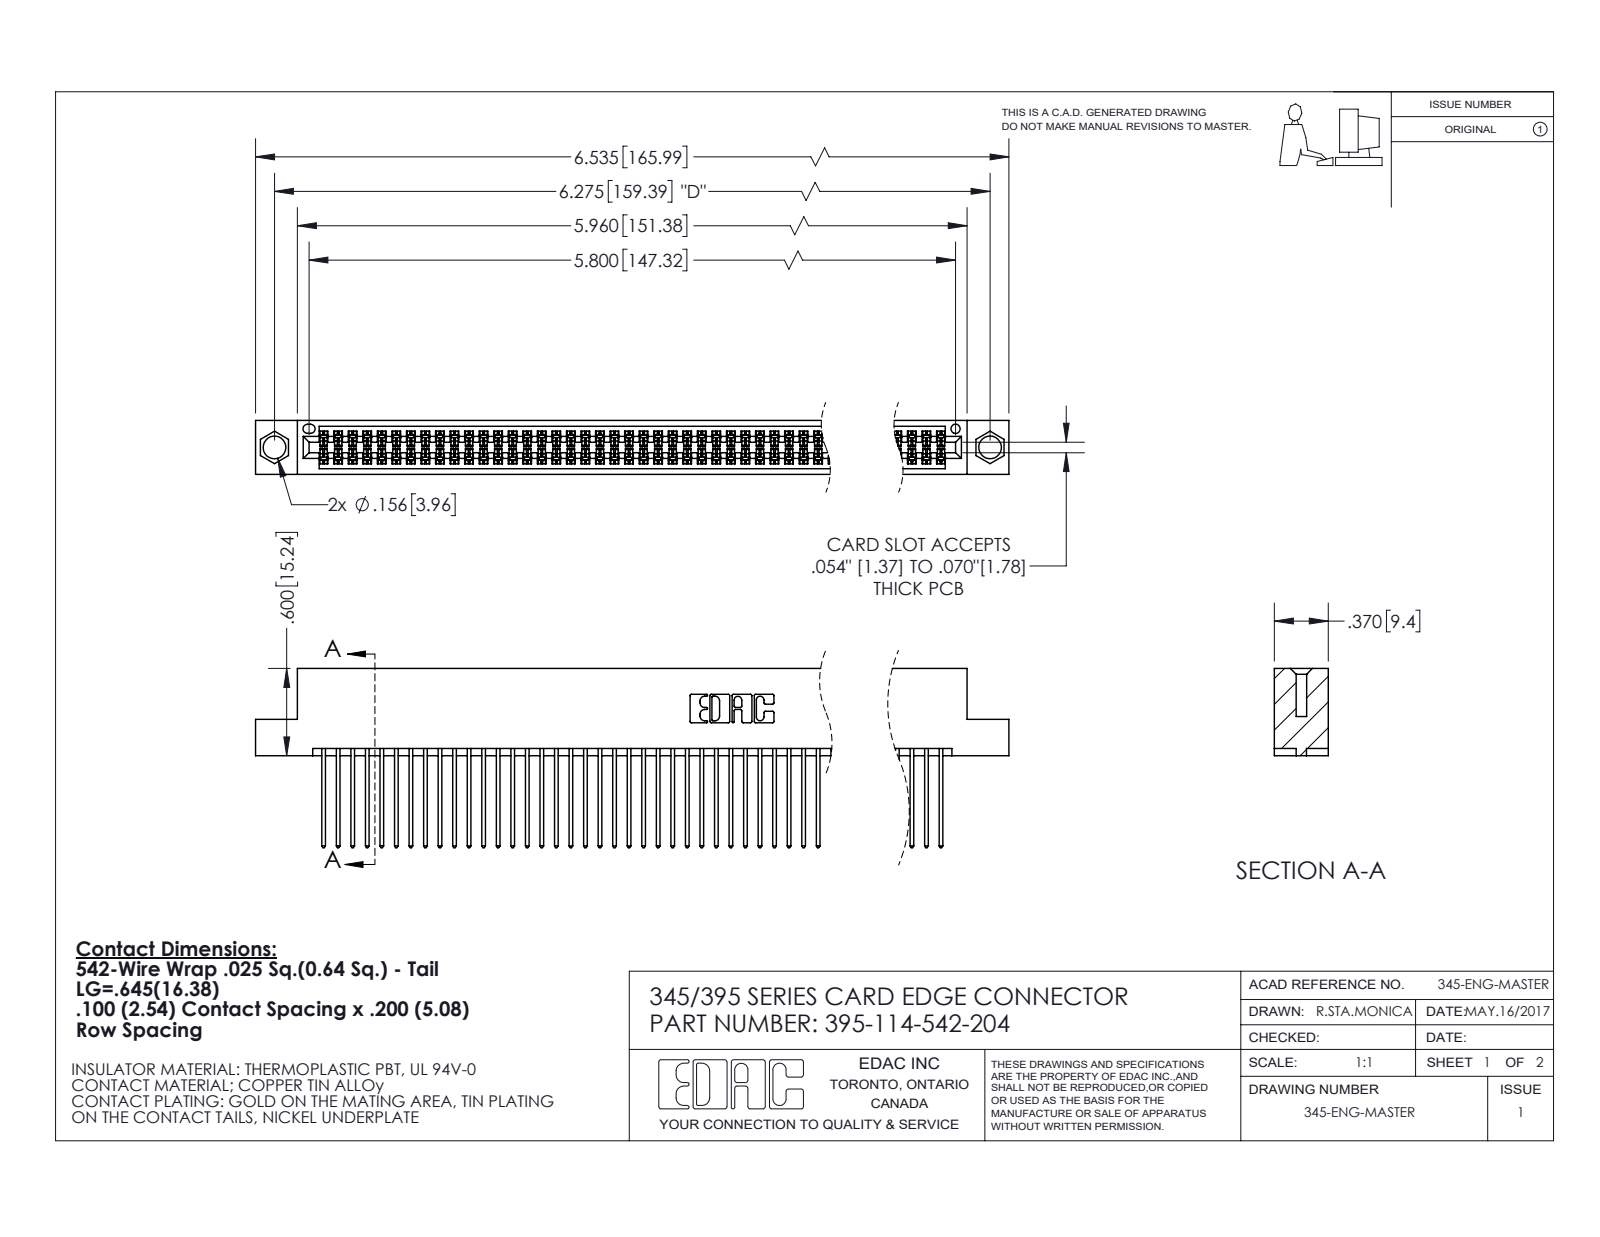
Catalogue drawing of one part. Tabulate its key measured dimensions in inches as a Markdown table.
| quantity | value |
| --- | --- |
| part name | 395-114-542-204; 345 Part_Flush Mounting Lugs - 0.156 Dia-TI; 345-292-001_345-293-142 |
| STEP written by | SolidWorks 2020 (CONFIG_CONTROL_DESIGN) |
| units | inches |
| bodies | 115 solids, 5840 faces (3856 planar, 1984 cylindrical, 0 other) |
| overall size | 6.535 × 1.232 × 0.37 |
| volume | 1.018 in³ |
| surface area | 42.31 in² |
| round holes (diameter × count) | 0.156 × 2, 0.064 × 1 |
| partial cylindrical surfaces (radius × count) | 0.006 × 171, 0.01 × 114, 0.01 × 22, 0.007 × 6, 0.031 × 6, 0.026 × 3, 0.014 × 2, 0.019 × 2 |
| main face-to-face distances | 0.298, 0.072, 0.2, 0.098, 0.272, 0.025, 0.225, 0.37, 0.175, 0.149 |
| hole center spacings | 0.27, 6.039, 6.275 |
